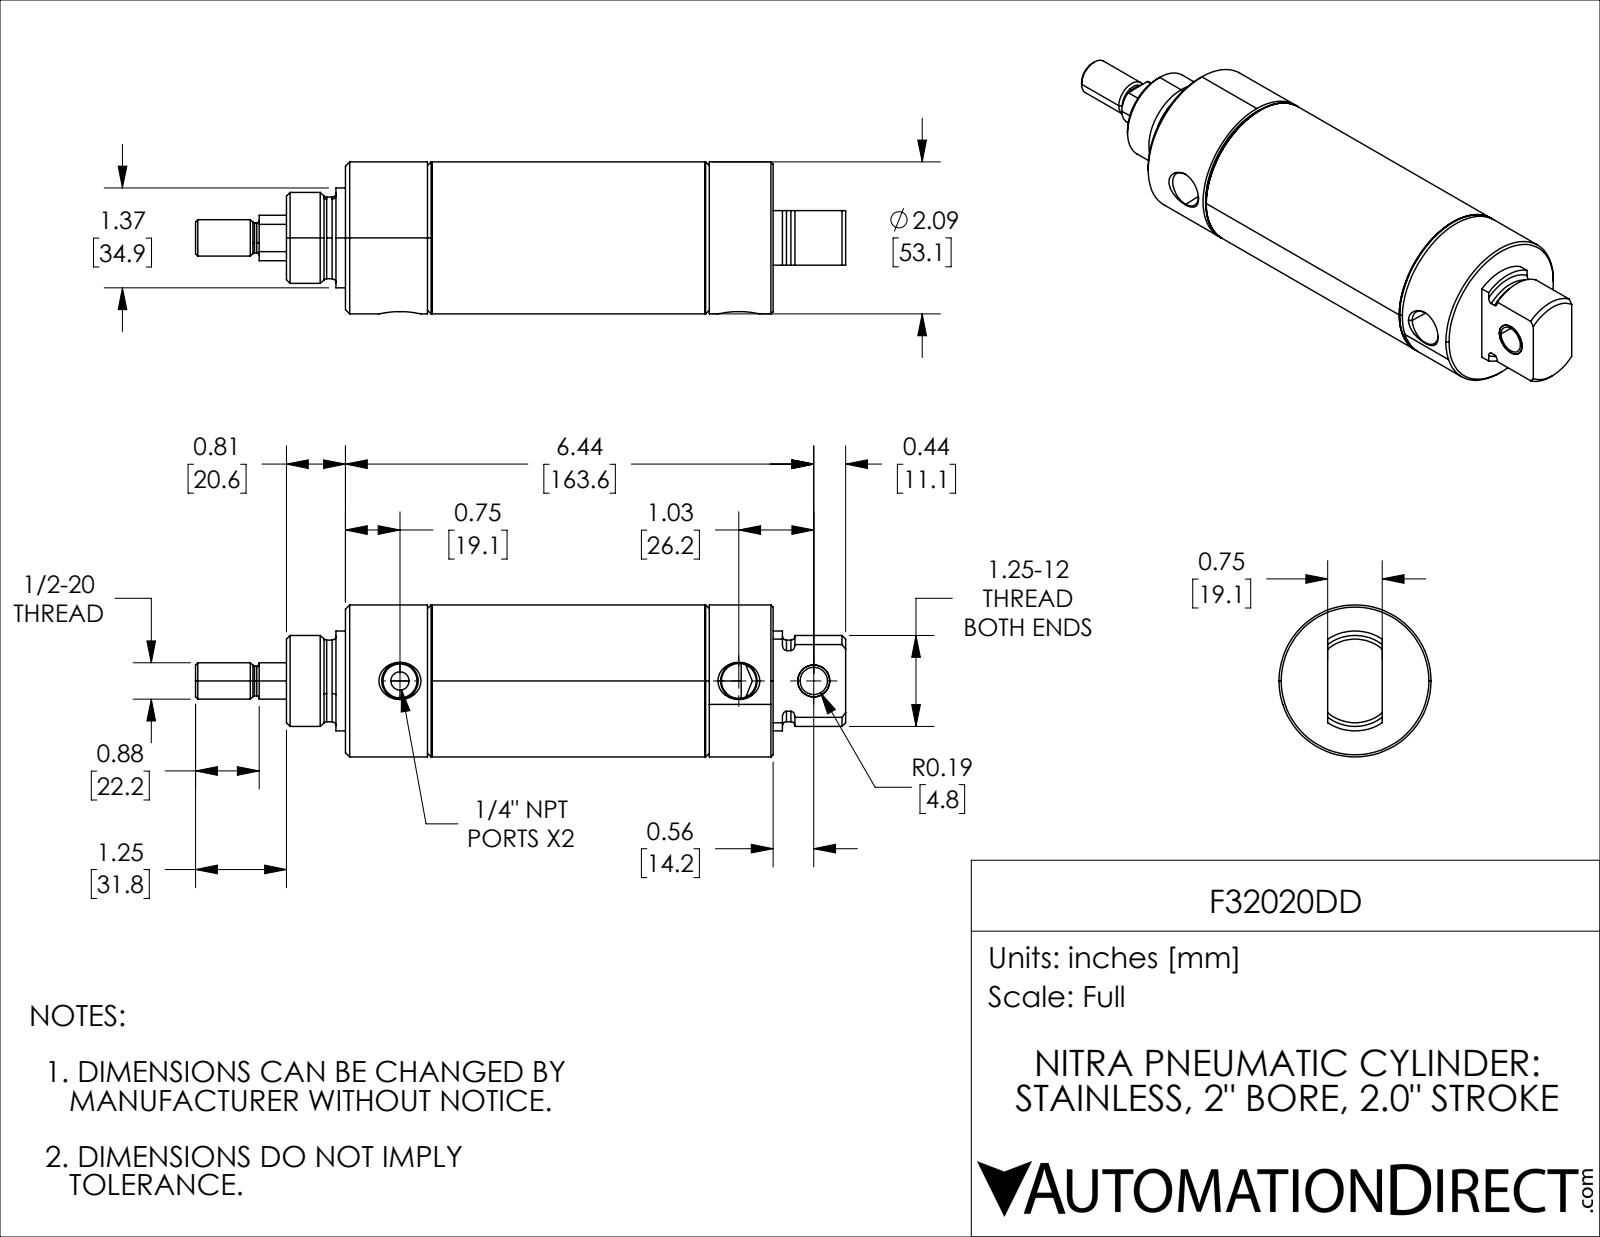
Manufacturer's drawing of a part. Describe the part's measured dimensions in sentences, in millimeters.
The part is named "F32020DD_11; F32020DD_3; F32020DD; F32020DD_7 (+2 more)". Its 3-D file was written by "SolidWorks 2021 (CONFIG_CONTROL_DESIGN)". It is 5 solids with 160 faces: 31 planar, 60 cylindrical and 69 other. Overall it measures 227.03 by 53.09 by 53.09 millimeters. Its volume is 253 845 cubic millimeters and its surface area 81 222 square millimeters. Round holes: 1 of diameter 6.35, 1 of diameter 9.55, 1 of diameter 11.15, 1 of diameter 12.18, 1 of diameter 16.52, 1 of diameter 19.05, 1 of diameter 49.05. Round bosses or shafts: 1 of diameter 53.09, 1 of diameter 51.16, 1 of diameter 34.87, 1 of diameter 31.75, 1 of diameter 28.51, 1 of diameter 15.88, 1 of diameter 12.7, 1 of diameter 10.46. Partial cylindrical surfaces (rounded edges, fillets, slot ends): 1 of radius 14.25. The main face-to-face distances are 30.17, 50.8, 80.97, 111.2, 60.4, 30.23, 38.15, 88.95, 119.12, 149.35. The hole center spacings are 26.16, 118.36, 144.52.
